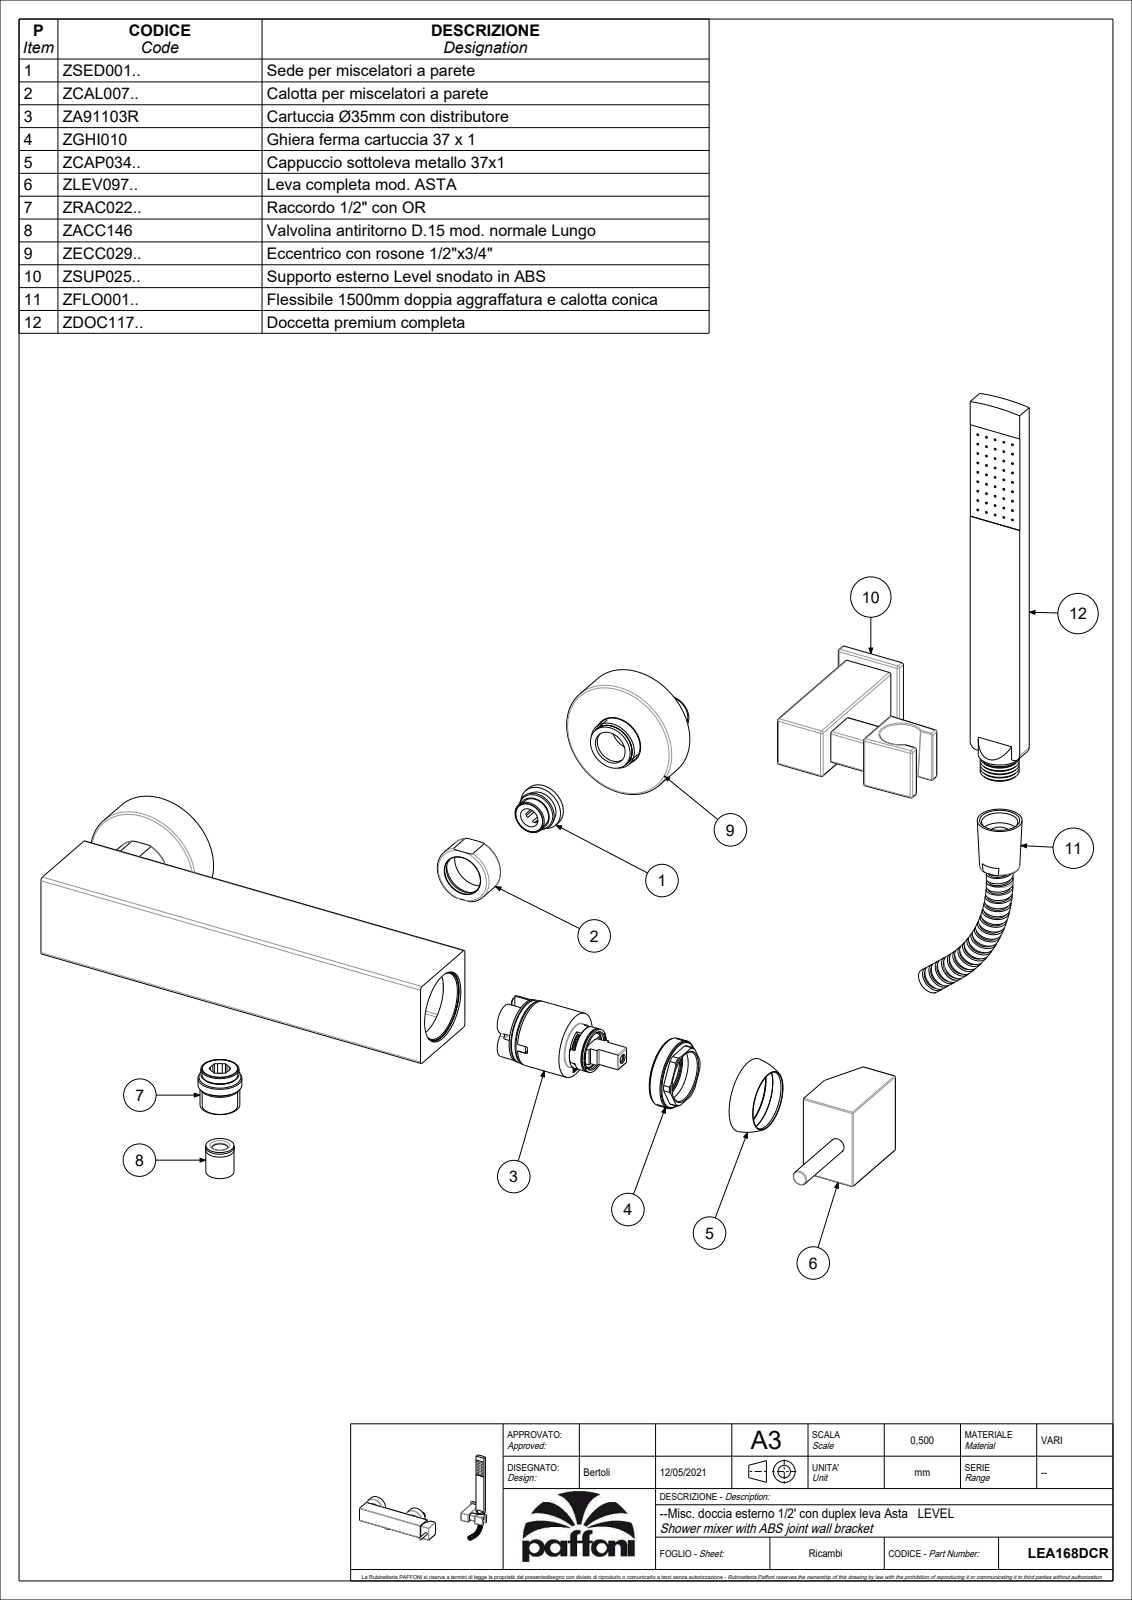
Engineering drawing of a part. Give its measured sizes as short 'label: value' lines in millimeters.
name: LEA168DCR
written by: CREO PARAMETRIC BY PTC INC, 2020044 (CONFIG_CONTROL_DESIGN)
unit: mm
bodies: 2 solids, 1978 faces (1042 planar, 526 cylindrical, 410 other)
size: 472.5 × 372 × 120.75
volume: 411 885 mm³; area: 220 774 mm²
holes: 4× ⌀12, 3× ⌀9, 2× ⌀4, 2× ⌀7, 2× ⌀8, 2× ⌀10.5, 2× ⌀18, 2× ⌀21.6, 2× ⌀24.5, 2× ⌀25, 2× ⌀37, 2× ⌀62.3
bosses: 11× ⌀2, 2× ⌀63.5, 2× ⌀27, 2× ⌀24, 2× ⌀17.7, 1× ⌀35, 1× ⌀34.8, 1× ⌀33.8
rounds: 122× R1, 60× R0.5, 11× R0.15, 9× R0.3, 4× R1.5, 4× R7, 2× R4, 2× R4.5
face distances: 3.75, 42.75, 46.5, 18.75, 39, 15, 3, 24, 27.75, 10
hole spacings: 0.71, 8.51, 8.6, 13.04, 13.21, 13.51, 6, 13
